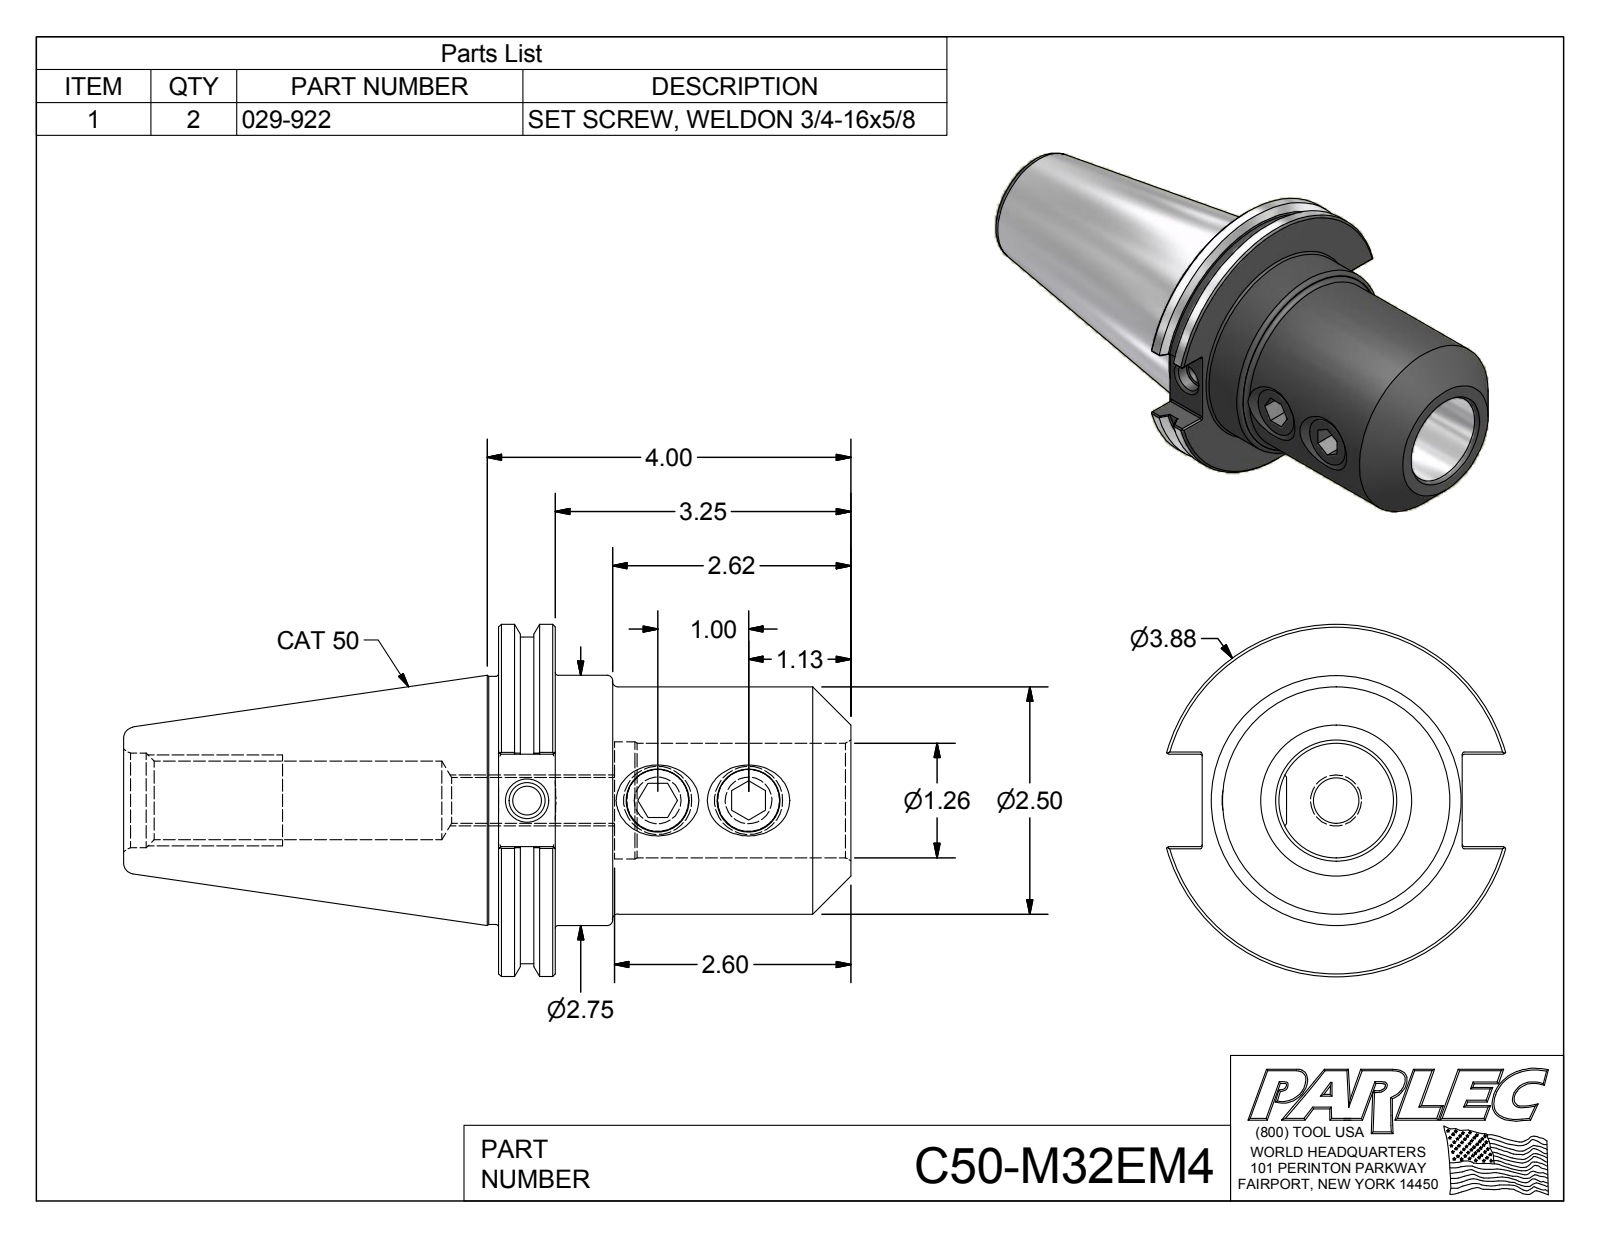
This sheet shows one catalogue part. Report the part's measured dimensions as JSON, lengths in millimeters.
{"part_name": "C50-M32EM4; C50-M32EM4-1; 029-922", "step_written_by": "Autodesk Inventor 2012 (AUTOMOTIVE_DESIGN)", "units": "millimeters", "bodies": {"solids": 3, "faces": 120, "planar": 51, "cylindrical": 32, "other": 37}, "overall_size": [203.2, 98.4, 94.7], "volume_mm3": 530800, "surface_area_mm2": 69810, "round_holes": [[17.3, 2], [8, 1], [10.1, 1], [12.8, 1], [22, 1], [26.4, 1], [32, 1], [32.8, 1]], "round_bosses_or_shafts": [[19.1, 2], [98.4, 1], [91.3, 1], [69.9, 1], [69.3, 1], [63.5, 1]], "partial_cylinders_radius": [[0.5, 12]], "face_to_face_distances": [15.9, 32.4, 16.5, 98.4, 82.6, 66, 64.9, 104.8, 120.7, 137.2], "hole_center_spacings": [25.4, 36.4, 61.8]}
